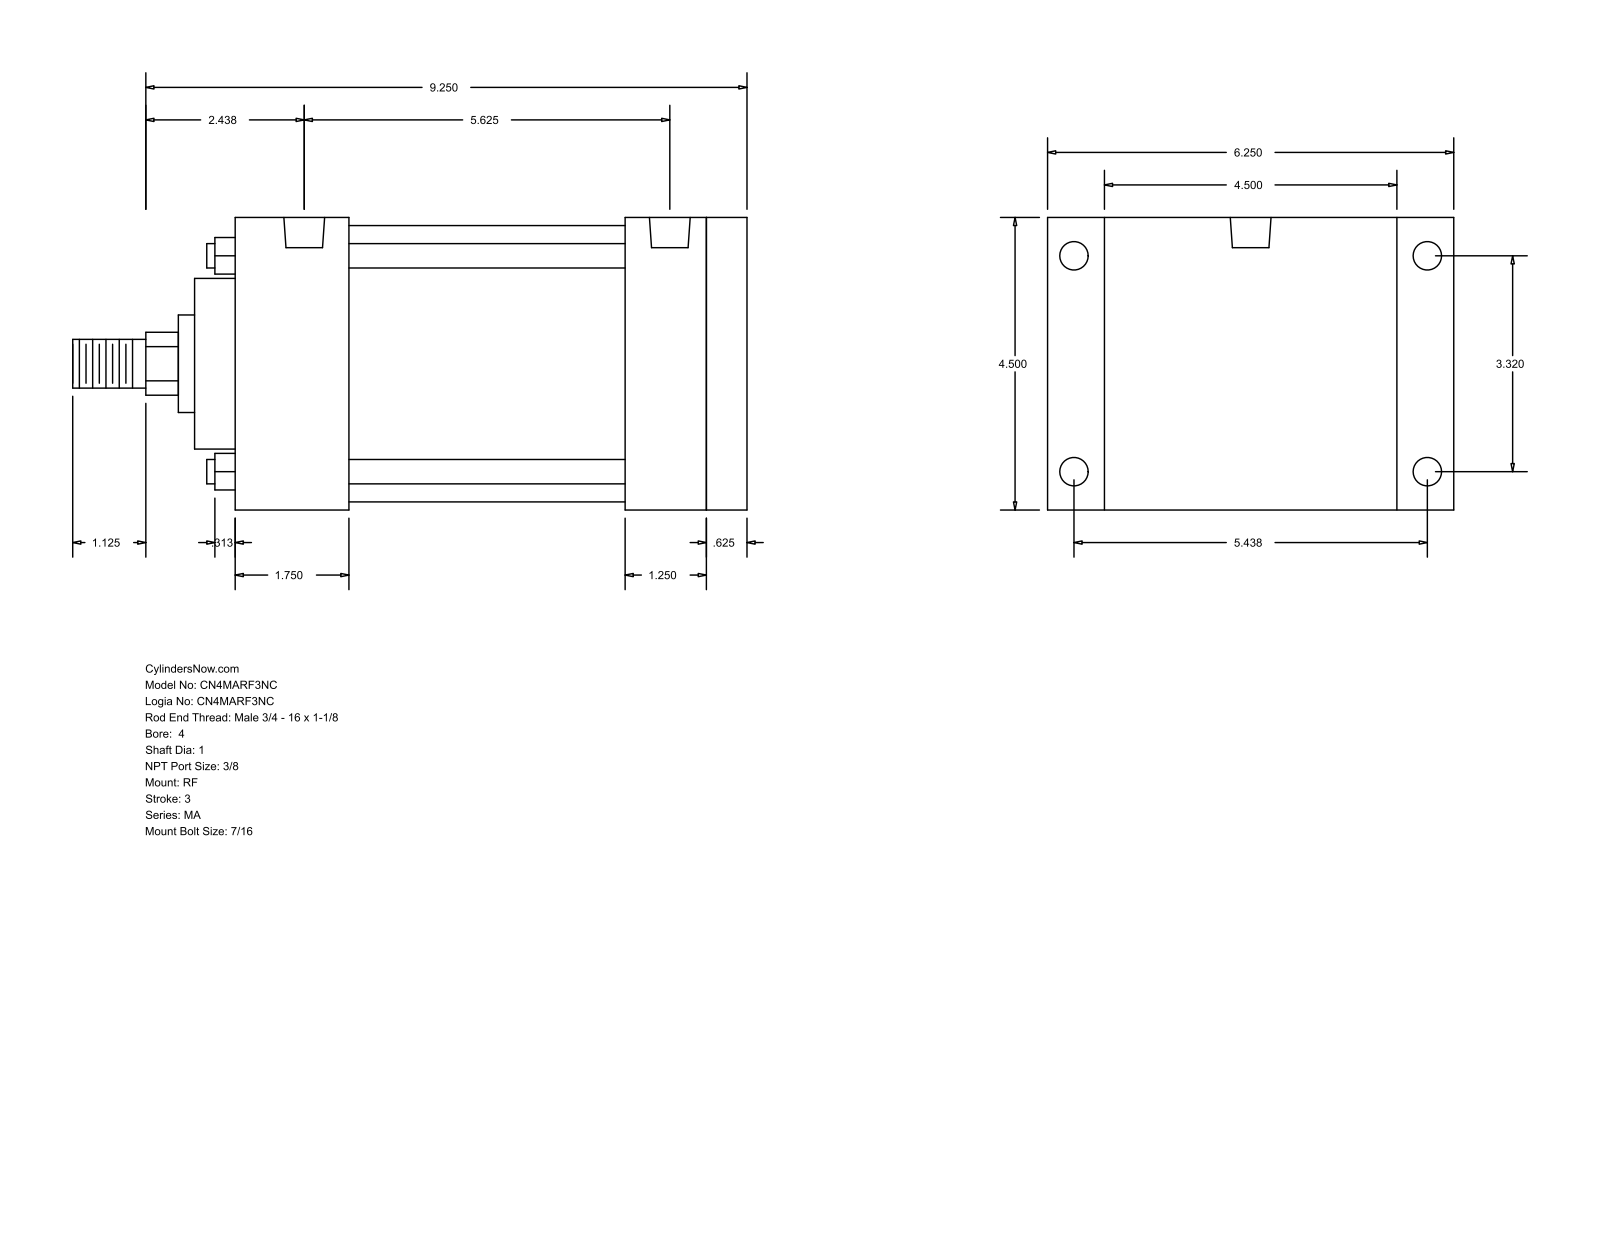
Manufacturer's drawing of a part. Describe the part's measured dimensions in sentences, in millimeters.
The part is named "MA_RF__0400_1". Its 3-D file was written by "GSSL Pune (CONFIG_CONTROL_DESIGN)". It is 0 solids with 94 faces: 65 planar, 29 cylindrical and 0 other. Overall it measures 263.52 by 158.75 by 114.3 millimeters. Round holes: 8 of diameter 11.11, 2 of diameter 15.93. Round bosses or shafts: 4 of diameter 9.53, 1 of diameter 107.95, 1 of diameter 66.67, 1 of diameter 38.1, 1 of diameter 25.4, 1 of diameter 19.05. Partial cylindrical surfaces (rounded edges, fillets, slot ends): 1 of radius 12.29. The main face-to-face distances are 114.3, 200.03, 184.15, 15.88, 22.23, 136.53, 152.4, 31.75, 47.63, 44.46. The hole center spacings are 138.12, 4.76, 84.32, 133.36, 161.82, 142.88.
